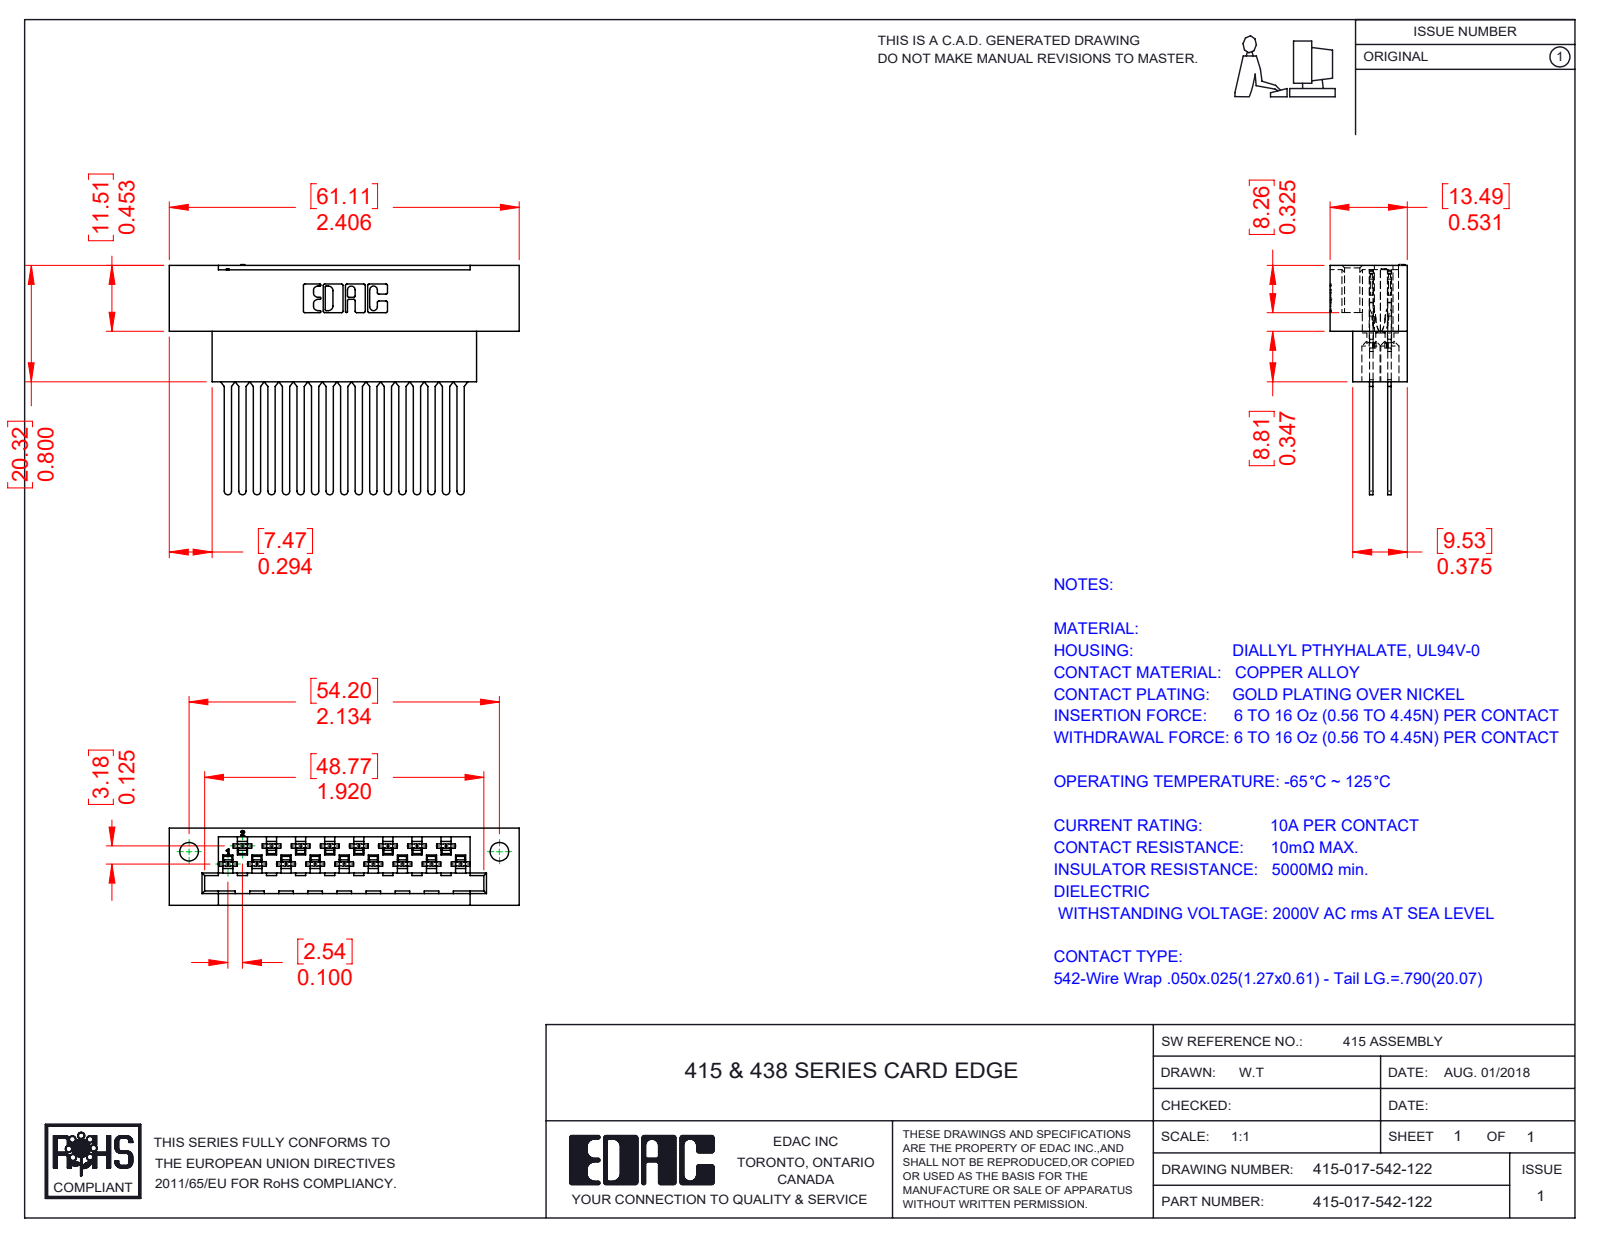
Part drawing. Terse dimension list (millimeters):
name: 516-290-001_542; 415-210-001_415-210-017-122; 415-017-542-122
written by: SolidWorks 2016 (CONFIG_CONTROL_DESIGN)
unit: mm
bodies: 18 solids, 1810 faces (1149 planar, 486 cylindrical, 175 other)
size: 61.11 × 40.17 × 13.49
volume: 10 079 mm³; area: 12 717 mm²
holes: 17× ⌀1.27, 17× ⌀3.3, 2× ⌀3.25
rounds: 68× R0.3, 68× R0.56, 34× R0.18, 34× R0.2, 34× R0.41, 34× R2.03, 22× R0.25, 17× R0.64
face distances: 3.18, 0.61, 13.49, 7.49, 6.61, 6.88, 6, 1.27, 1.88, 2.82
hole spacings: 5.08, 10.16, 15.24, 20.32, 2.54, 4.06, 7.62, 8.25
